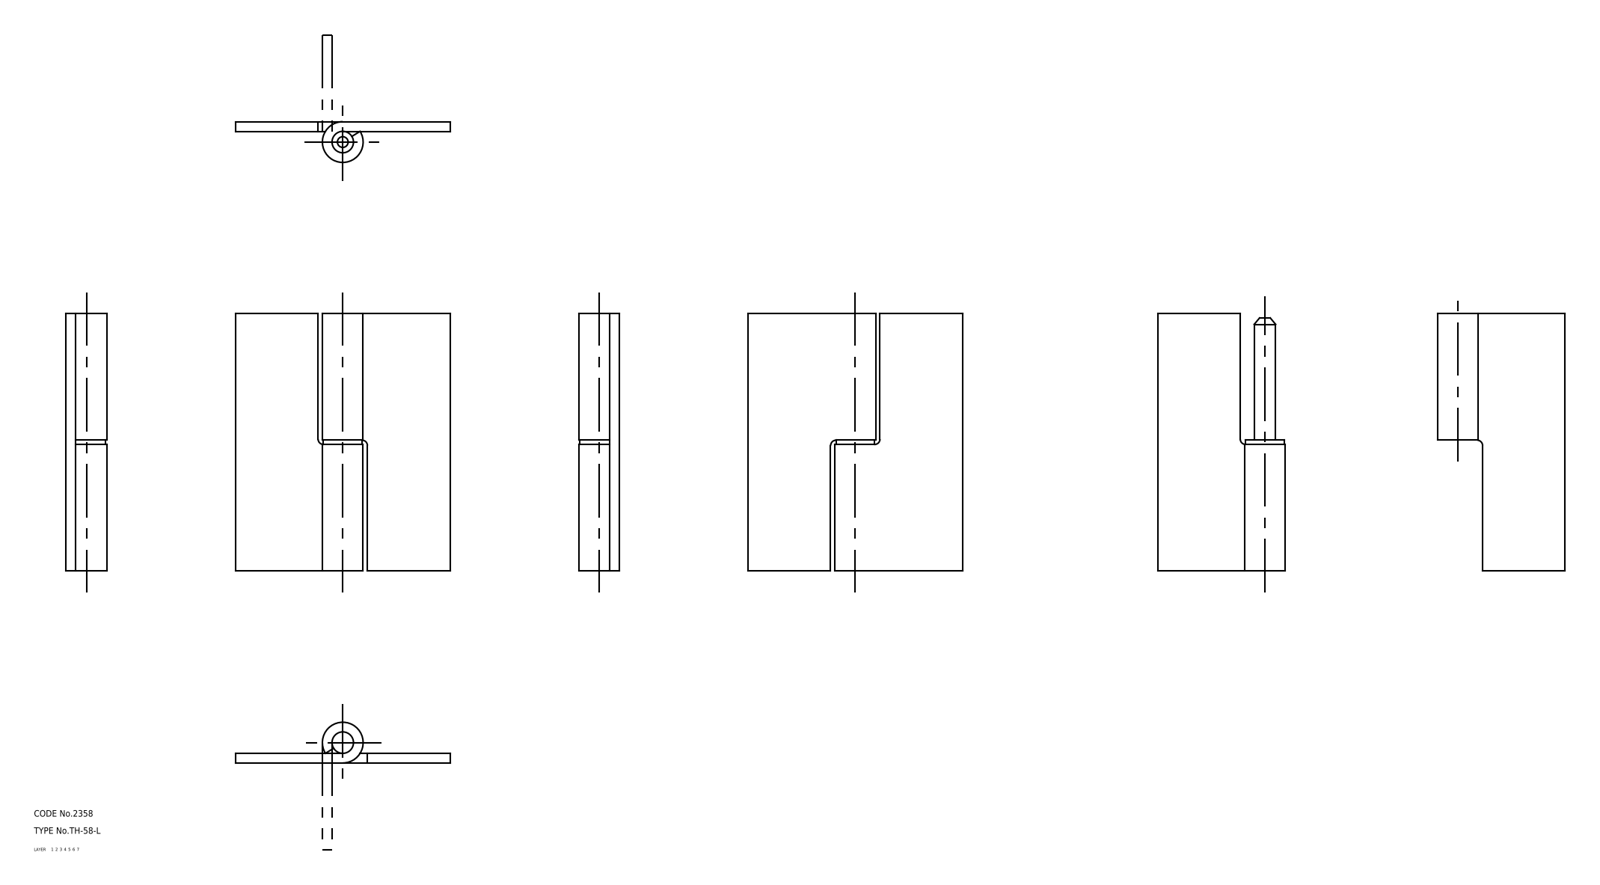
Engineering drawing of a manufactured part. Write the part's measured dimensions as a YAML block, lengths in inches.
part_name: "washer; shaft; hinge piece_B; hinge piece_A (+1 more)"
step_written_by: "CADfix (AUTOMOTIVE_DESIGN)"
units: inches
bodies: {solids: 4, faces: 32, planar: 0, cylindrical: 0, other: 32}
overall_size: [4.724, 3.937, 0.748]
volume: 4.728
surface_area: 59.31
